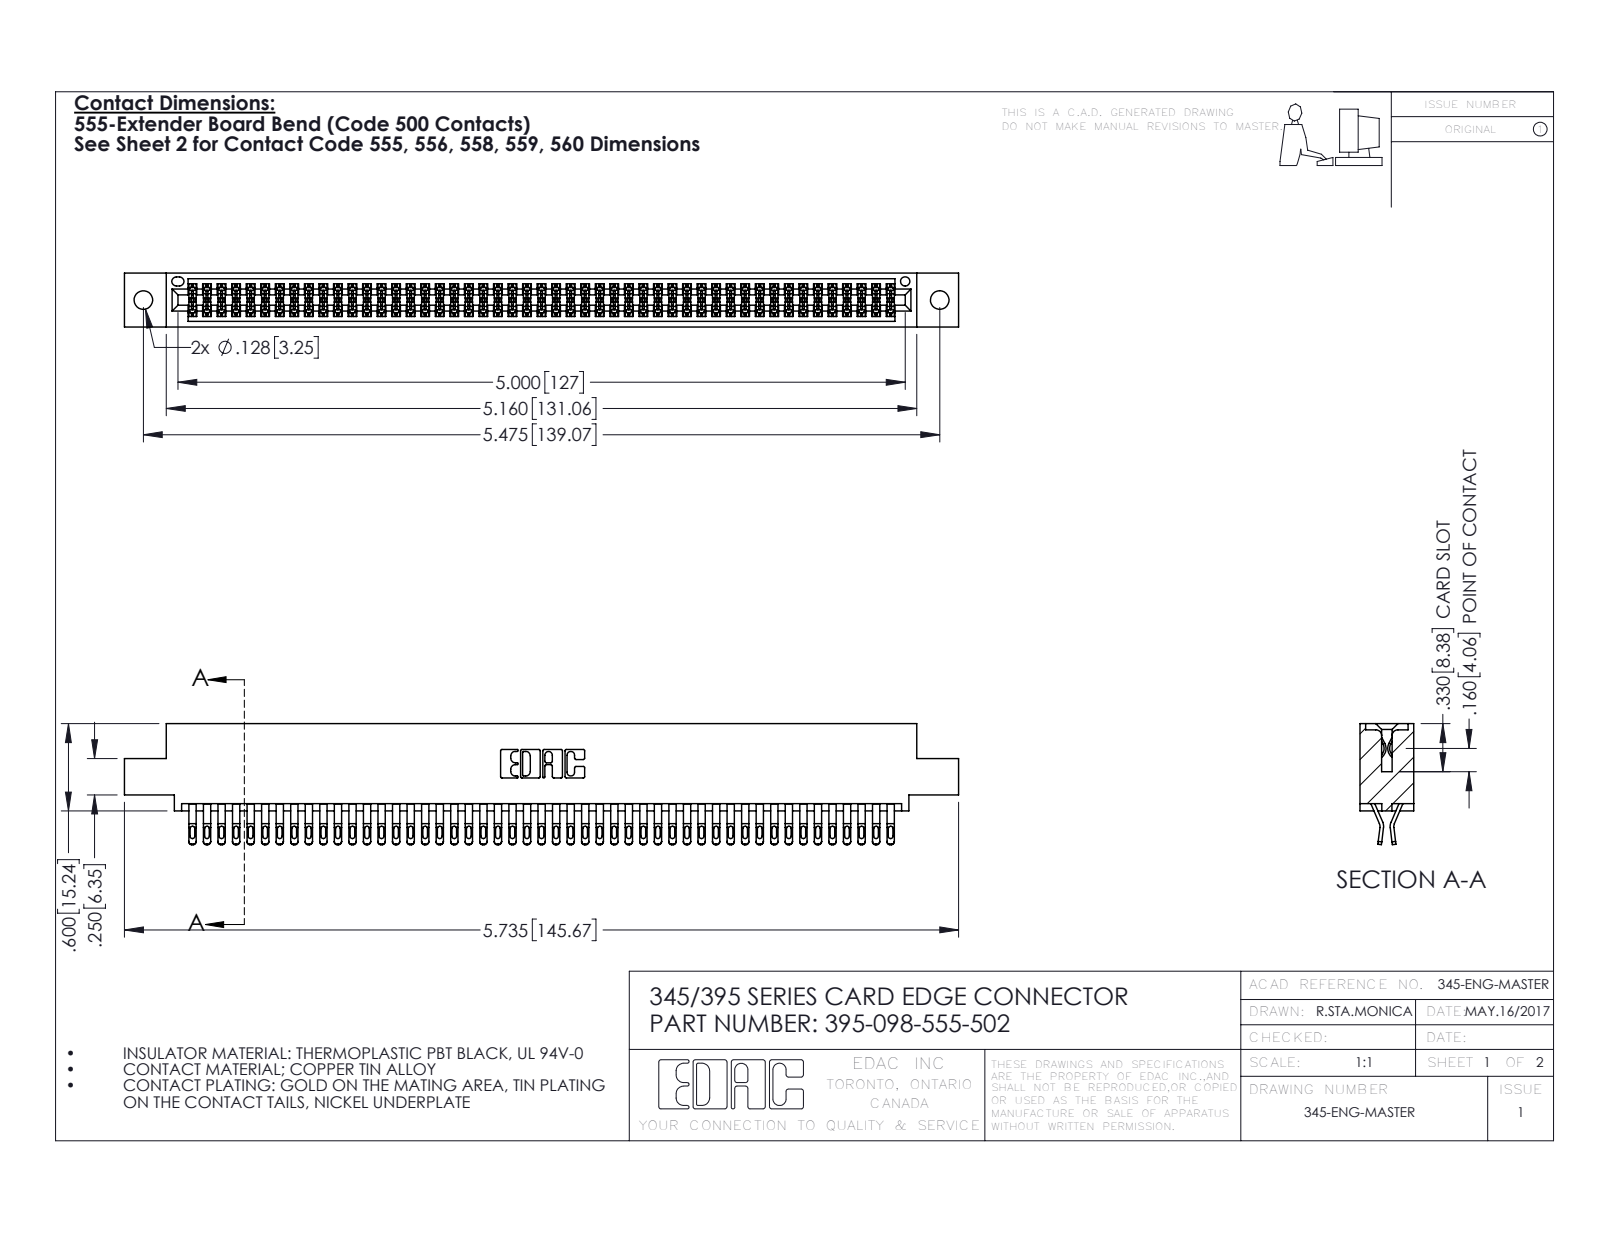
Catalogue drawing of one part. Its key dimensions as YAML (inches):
part_name: "345 Part_0.110 Offset - 0.128 Dia; 395-098-555-502; 345-292-001_555 Tail"
step_written_by: "SolidWorks 2016 (CONFIG_CONTROL_DESIGN)"
units: inches
bodies: {solids: 99, faces: 5618, planar: 3122, cylindrical: 2496, other: 0}
overall_size: [5.735, 0.832, 0.37]
volume: 0.878
surface_area: 34.43
round_holes:
  - {diameter: 0.128, count: 2}
  - {diameter: 0.064, count: 1}
partial_cylinders:
  - {radius: 0.016, count: 245}
  - {radius: 0.02, count: 196}
  - {radius: 0.006, count: 147}
  - {radius: 0.01, count: 22}
  - {radius: 0.007, count: 6}
  - {radius: 0.031, count: 6}
  - {radius: 0.026, count: 3}
  - {radius: 0.01, count: 2}
face_to_face_distances: [0.298, 0.072, 0.025, 0.37, 0.2, 0.098, 0.272, 0.225, 0.175, 0.149]
hole_center_spacings: [0.27, 5.239, 5.475]
